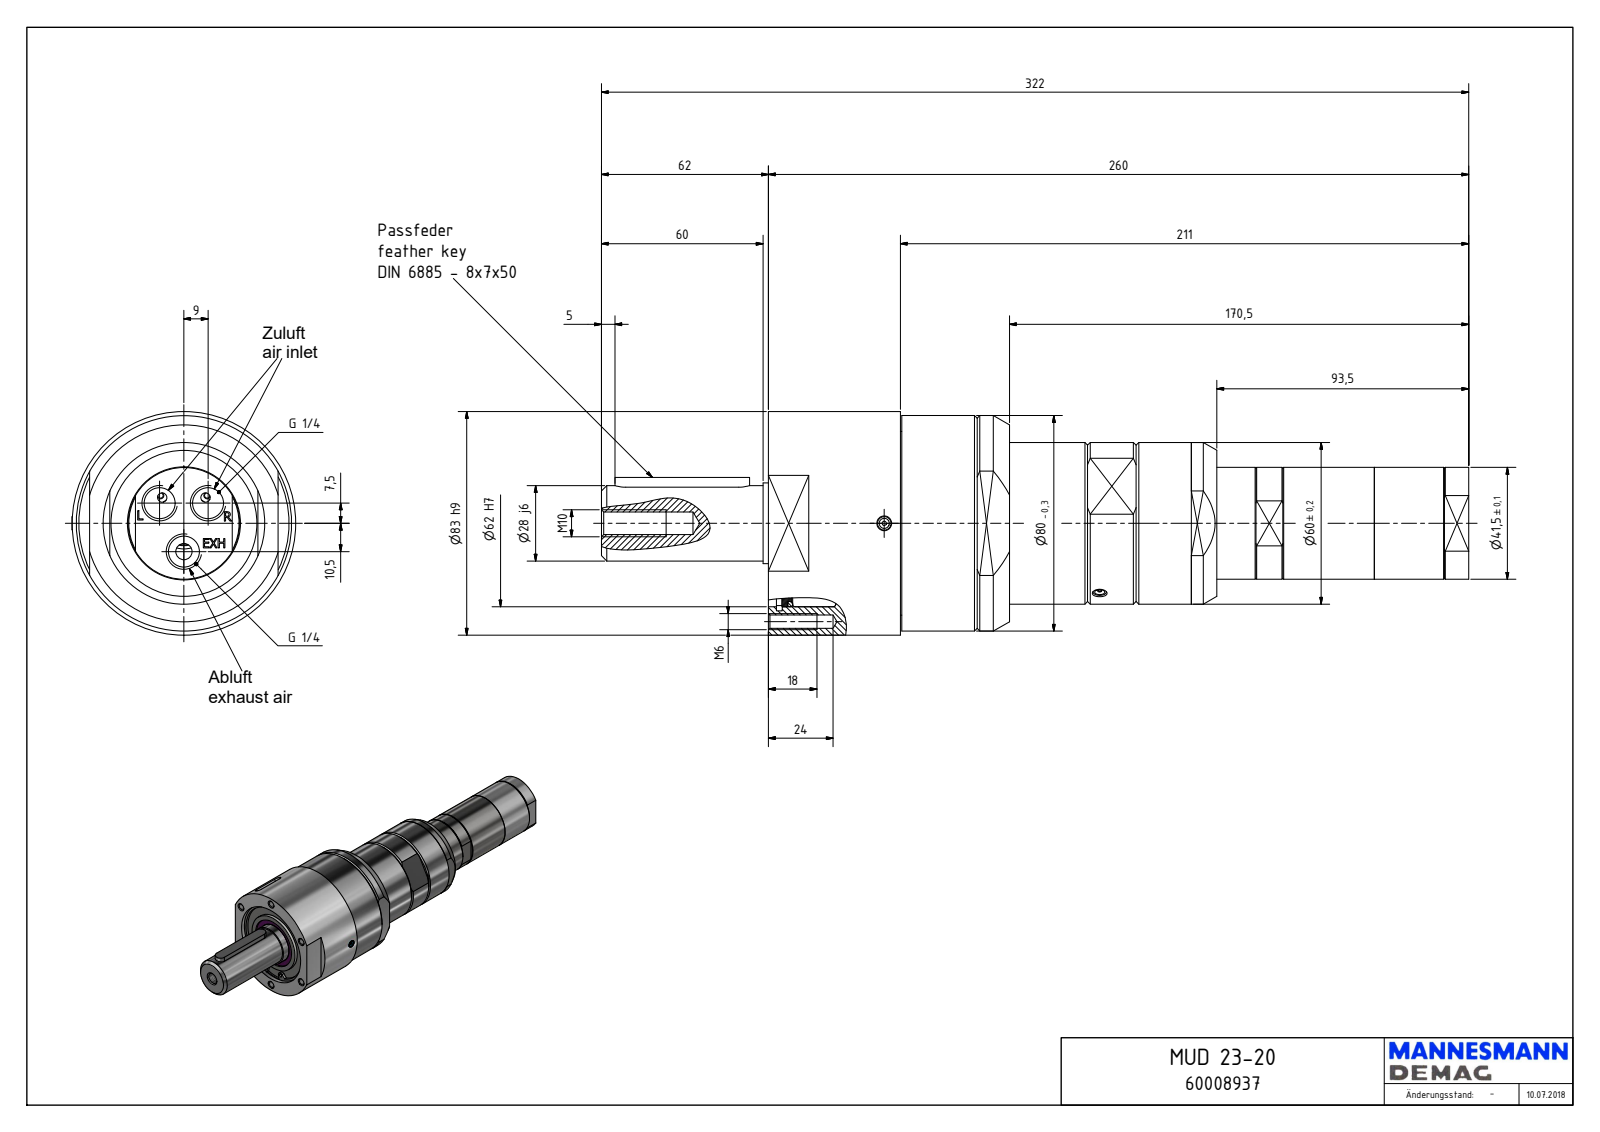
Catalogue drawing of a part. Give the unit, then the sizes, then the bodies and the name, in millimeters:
Units: millimetres
Overall size (bounding box): 322 × 83 × 83
Round holes (diameter × count): ⌀4.92 ×6, ⌀11.45 ×3, ⌀1.55 ×2, ⌀2.5 ×2, ⌀4 ×2, ⌀5.5 ×2, ⌀8.38 ×1, ⌀38 ×1, ⌀40 ×1, ⌀42 ×1, ⌀58.69 ×1, ⌀62 ×1
Round bosses / shafts (diameter × count): ⌀5 ×2, ⌀3.6 ×2, ⌀83 ×1, ⌀80 ×1, ⌀68.18 ×1, ⌀67 ×1, ⌀60 ×1, ⌀45 ×1
Partial cylindrical surfaces — rounded edges, fillets, slot ends (radius × count): R2.25 ×2, R3 ×2, R4 ×2, R32.5 ×2, R25.55 ×1, R28.04 ×1, R33.2 ×1
Main face-to-face distances: 49, 0.5, 89.5, 40.5, 2.5, 4.08, 44.92, 85.42, 46.5, 49.5
Hole centre spacings: 36.5, 63.22, 73, 11.72, 20.12, 25.04, 26.98, 30.36
Volume: 821 763 mm³ · Surface area: 77 874 mm²
Bodies: 1 solid, 265 faces (131 planar, 69 cylindrical, 65 other)
Part name (STEP PRODUCT): MUD 23-20_60008937
STEP written by: Autodesk Inventor 2018 (AUTOMOTIVE_DESIGN)
